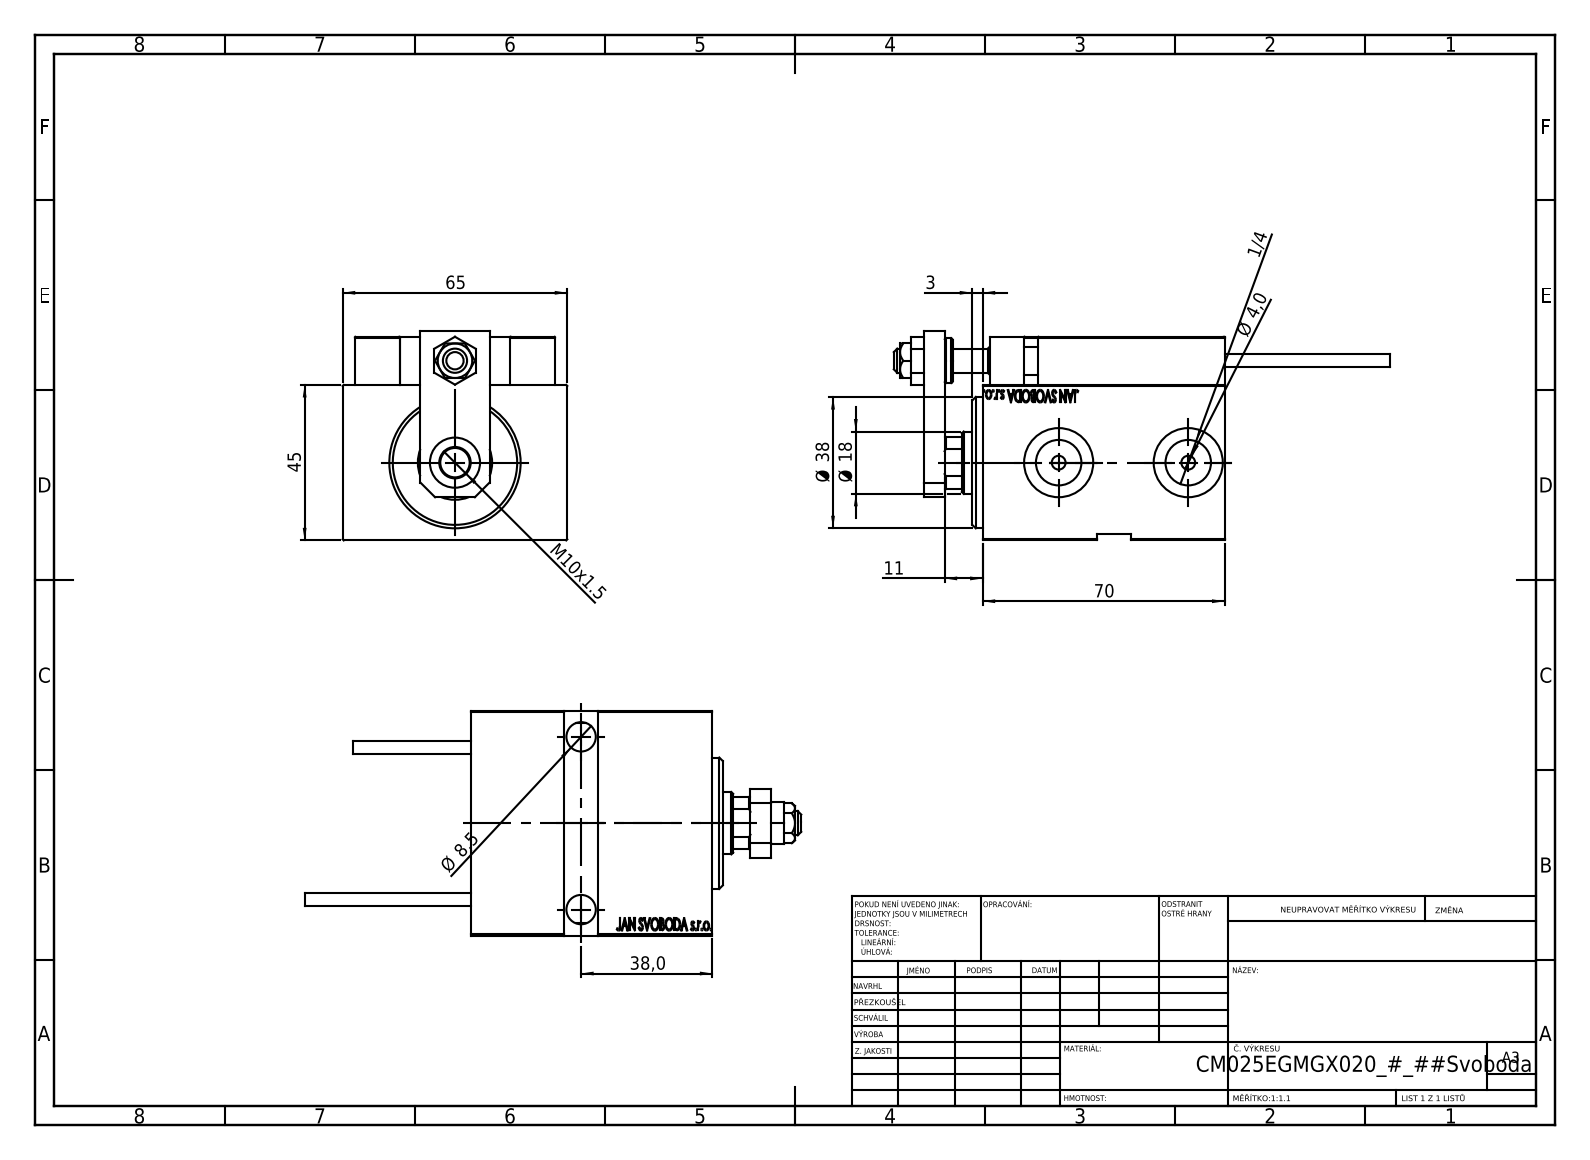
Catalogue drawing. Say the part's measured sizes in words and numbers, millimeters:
The part is named "Block; TYC_L79; SWITCH_X_FRONT_BACK; SWITCH DIM B,W (+7 more)". Its 3-D file was written by "SolidWorks 2019 (CONFIG_CONTROL_DESIGN)". It is 24 solids with 1283 faces: 568 planar, 174 cylindrical and 541 other. Overall it measures 143.7 by 65 by 60.5 millimeters. Its volume is 236 688 cubic millimeters and its surface area 63 453 square millimeters. Round holes: 6 of diameter 4, 5 of diameter 8, 4 of diameter 3.2, 3 of diameter 8.5, 2 of diameter 5, 2 of diameter 13.16, 2 of diameter 13.5, 2 of diameter 20, 1 of diameter 7, 1 of diameter 14.5, 1 of diameter 18, 1 of diameter 21.5. Round bosses or shafts: 2 of diameter 5, 2 of diameter 3.8, 1 of diameter 38, 1 of diameter 27, 1 of diameter 13, 1 of diameter 11. Partial cylindrical surfaces (rounded edges, fillets, slot ends): 30 of radius 0.3, 2 of radius 3, 1 of radius 8.5. The main face-to-face distances are 45, 65, 14, 59, 6, 19, 8, 13, 70, 3.5. The hole center spacings are 11.37, 20, 22.09, 29.59, 29.69, 30.89, 31.11, 34.17.
